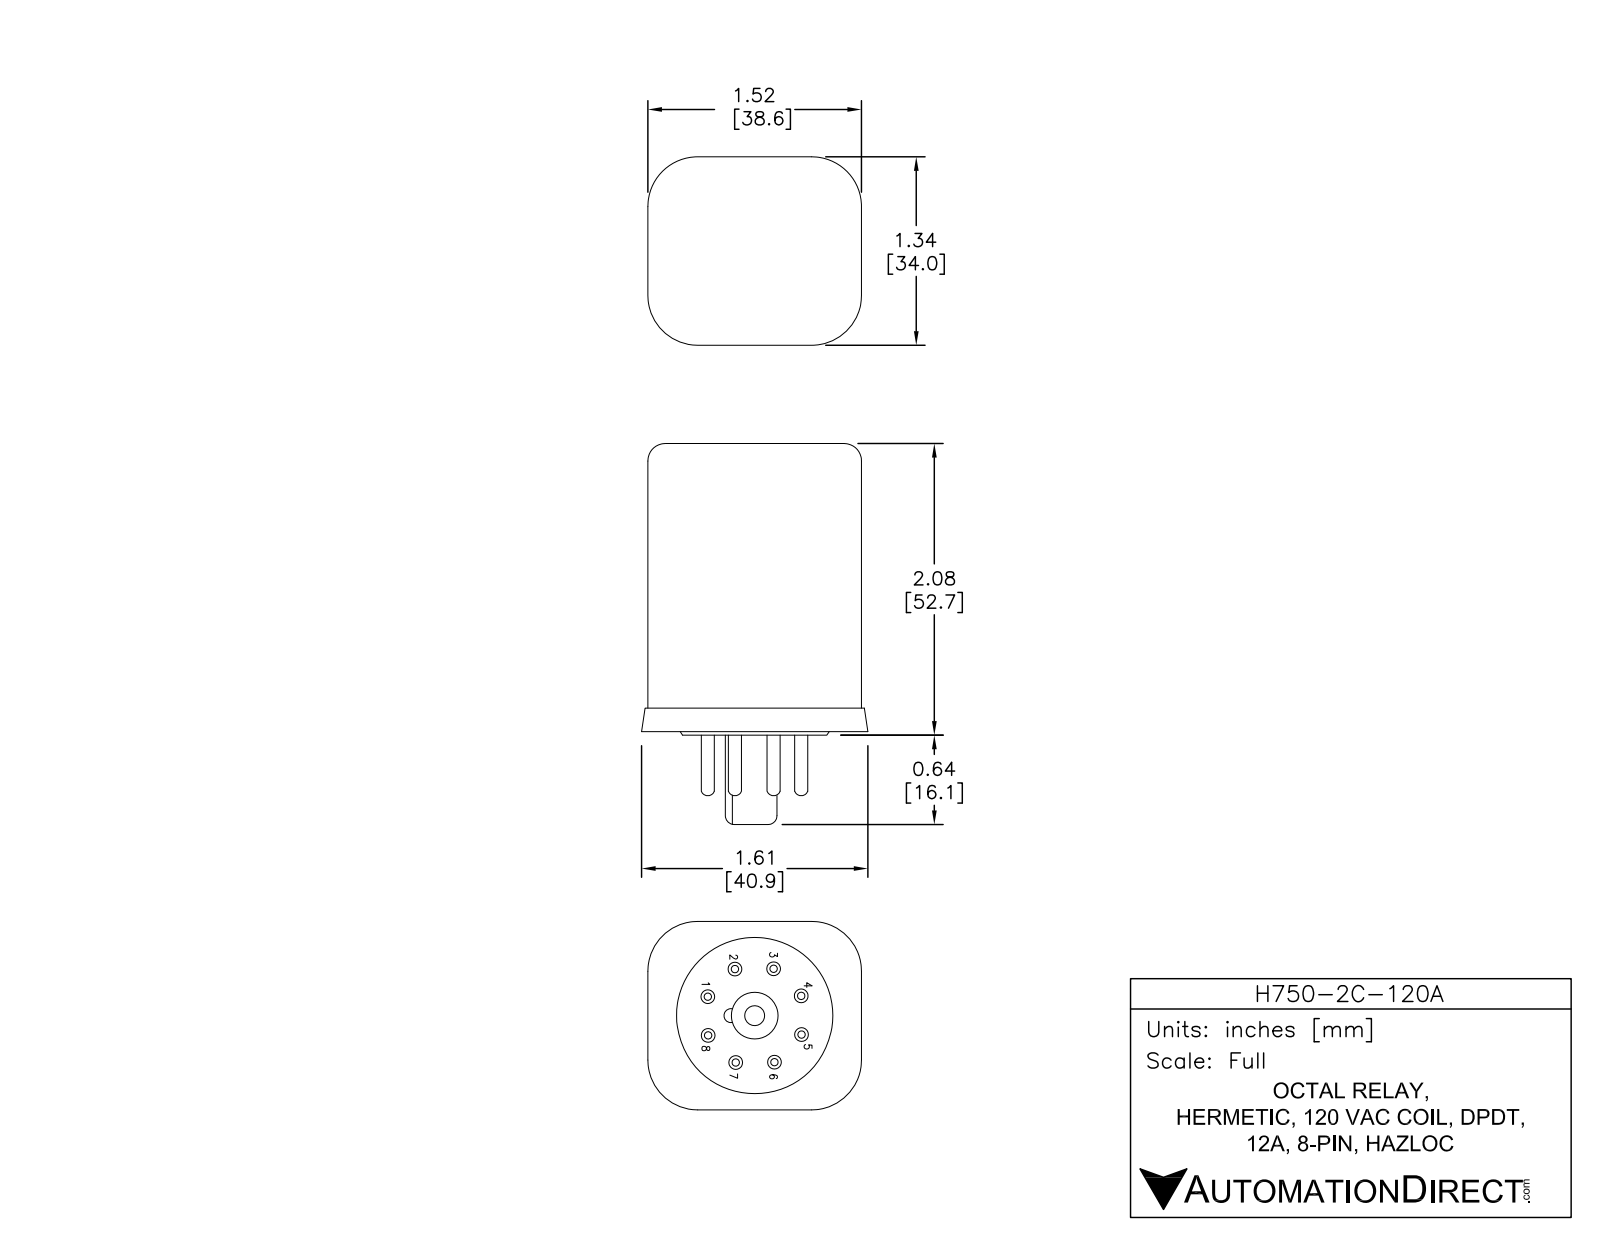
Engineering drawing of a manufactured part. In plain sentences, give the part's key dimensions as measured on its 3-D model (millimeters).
The part is named "H750-2C-120A". Its 3-D file was written by "SolidWorks 2013 (AUTOMOTIVE_DESIGN)". It is 13 solids with 287 faces: 124 planar, 65 cylindrical and 98 other. Overall it measures 67.3 by 41.35 by 36.6 millimeters. Its volume is 66 961 cubic millimeters and its surface area 10 747 square millimeters. Round holes: 8 of diameter 4.5, 1 of diameter 3.9. Round bosses or shafts: 8 of diameter 2.31, 1 of diameter 27, 1 of diameter 12, 1 of diameter 8. Partial cylindrical surfaces (rounded edges, fillets, slot ends): 8 of radius 0.62, 4 of radius 2.5, 4 of radius 10, 4 of radius 11.3, 2 of radius 0.5, 1 of radius 0.59. The main face-to-face distances are 53, 34, 38.75, 0.5, 53.5, 1.3, 35.3, 40.05, 1, 54. The hole center spacings are 8.5, 12.02, 15.7, 6.5, 6.51, 16.99.
